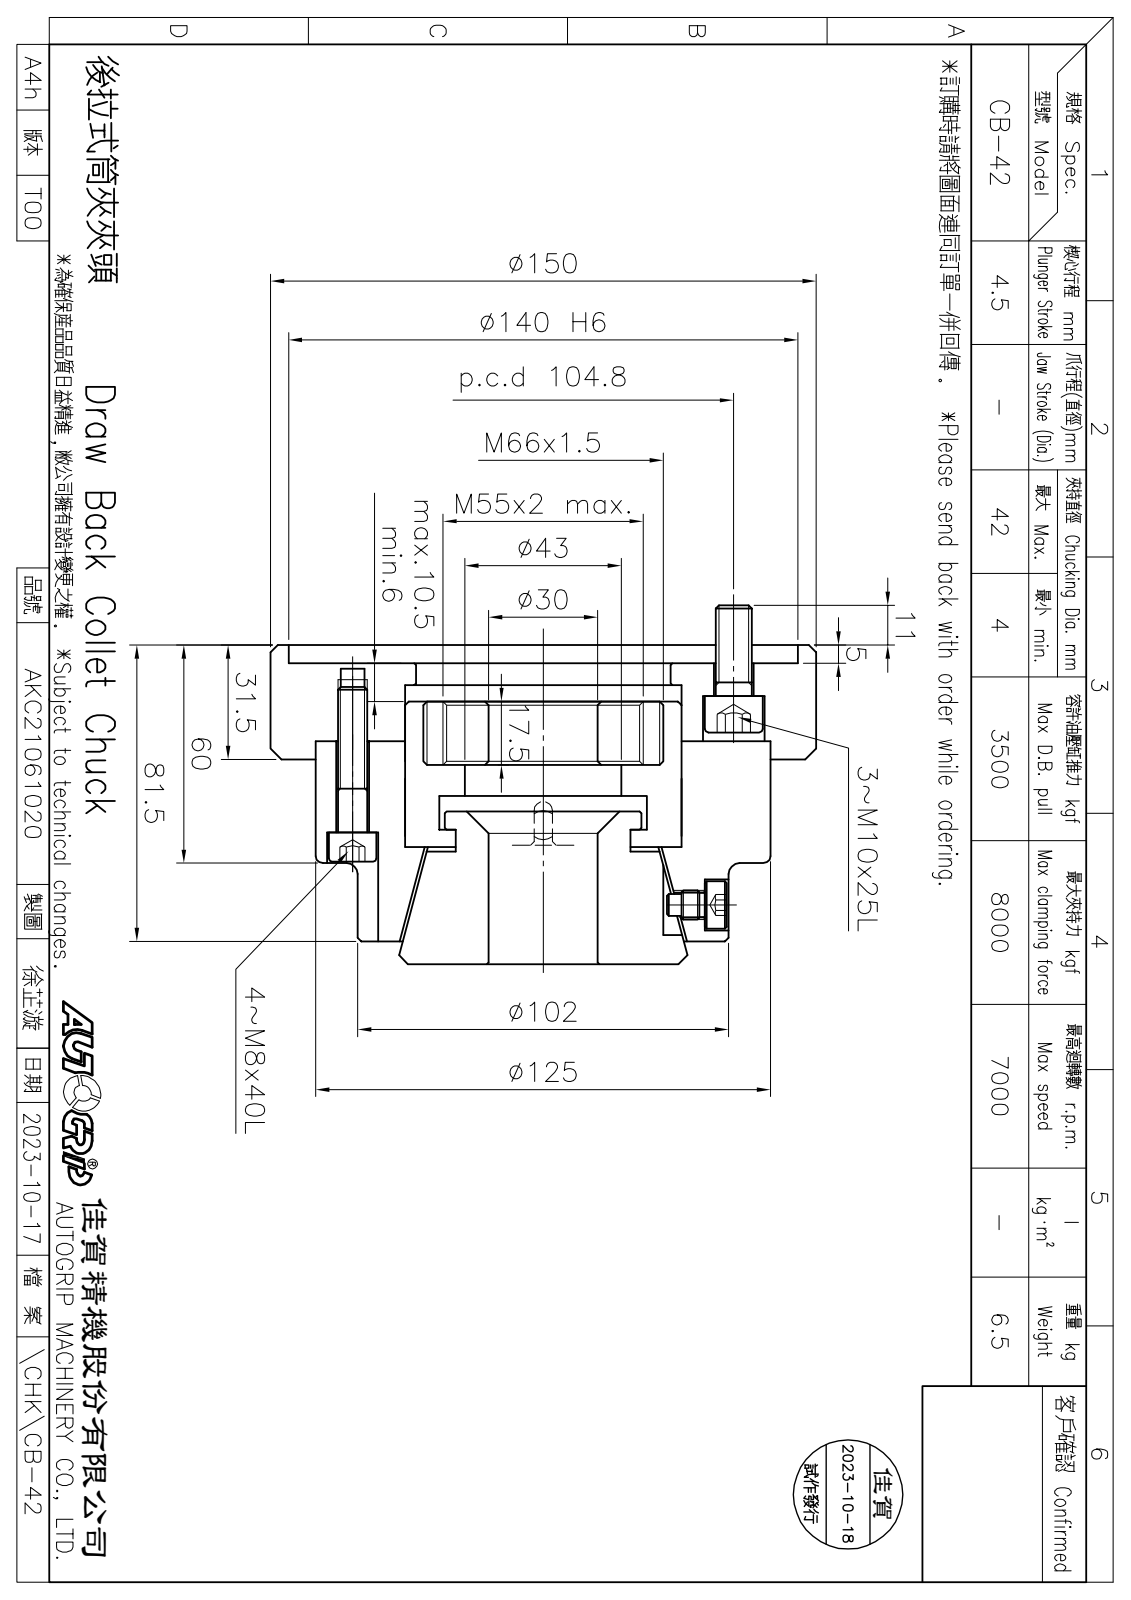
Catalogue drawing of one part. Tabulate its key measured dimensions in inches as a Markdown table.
| quantity | value |
| --- | --- |
| part name | CF-CB-42-02010; CF-CB-42-01010; CF-CB-42; 圓頭內六角螺栓_M8x40 (+3 more) |
| STEP written by | SolidWorks 2020 (CONFIG_CONTROL_DESIGN) |
| units | inches |
| bodies | 11 solids, 375 faces (134 planar, 123 cylindrical, 118 other) |
| overall size | 5.906 × 5.906 × 3.886 |
| volume | 53.41 in³ |
| surface area | 255.2 in² |
| round holes (diameter × count) | 0.197 × 8, 0.268 × 4, 0.354 × 4, 0.551 × 4, 0.335 × 3, 0.433 × 3, 0.669 × 3, 1.169 × 1, 1.693 × 1, 1.969 × 1, 2.087 × 1, 2.244 × 1 |
| round bosses / shafts (diameter × count) | 0.512 × 4, 0.315 × 4, 0.63 × 3, 0.394 × 3, 5.906 × 1, 4.016 × 1, 2.126 × 1, 1.909 × 1 |
| main face-to-face distances | 0.846, 1.043, 0.197, 2.165, 0.945, 0.433, 1.988, 1.142, 1.024, 3.256 |
| hole center spacings | 1.492, 1.61, 3.063, 3.544, 3.733, 2.063, 2.283, 0.201 |
